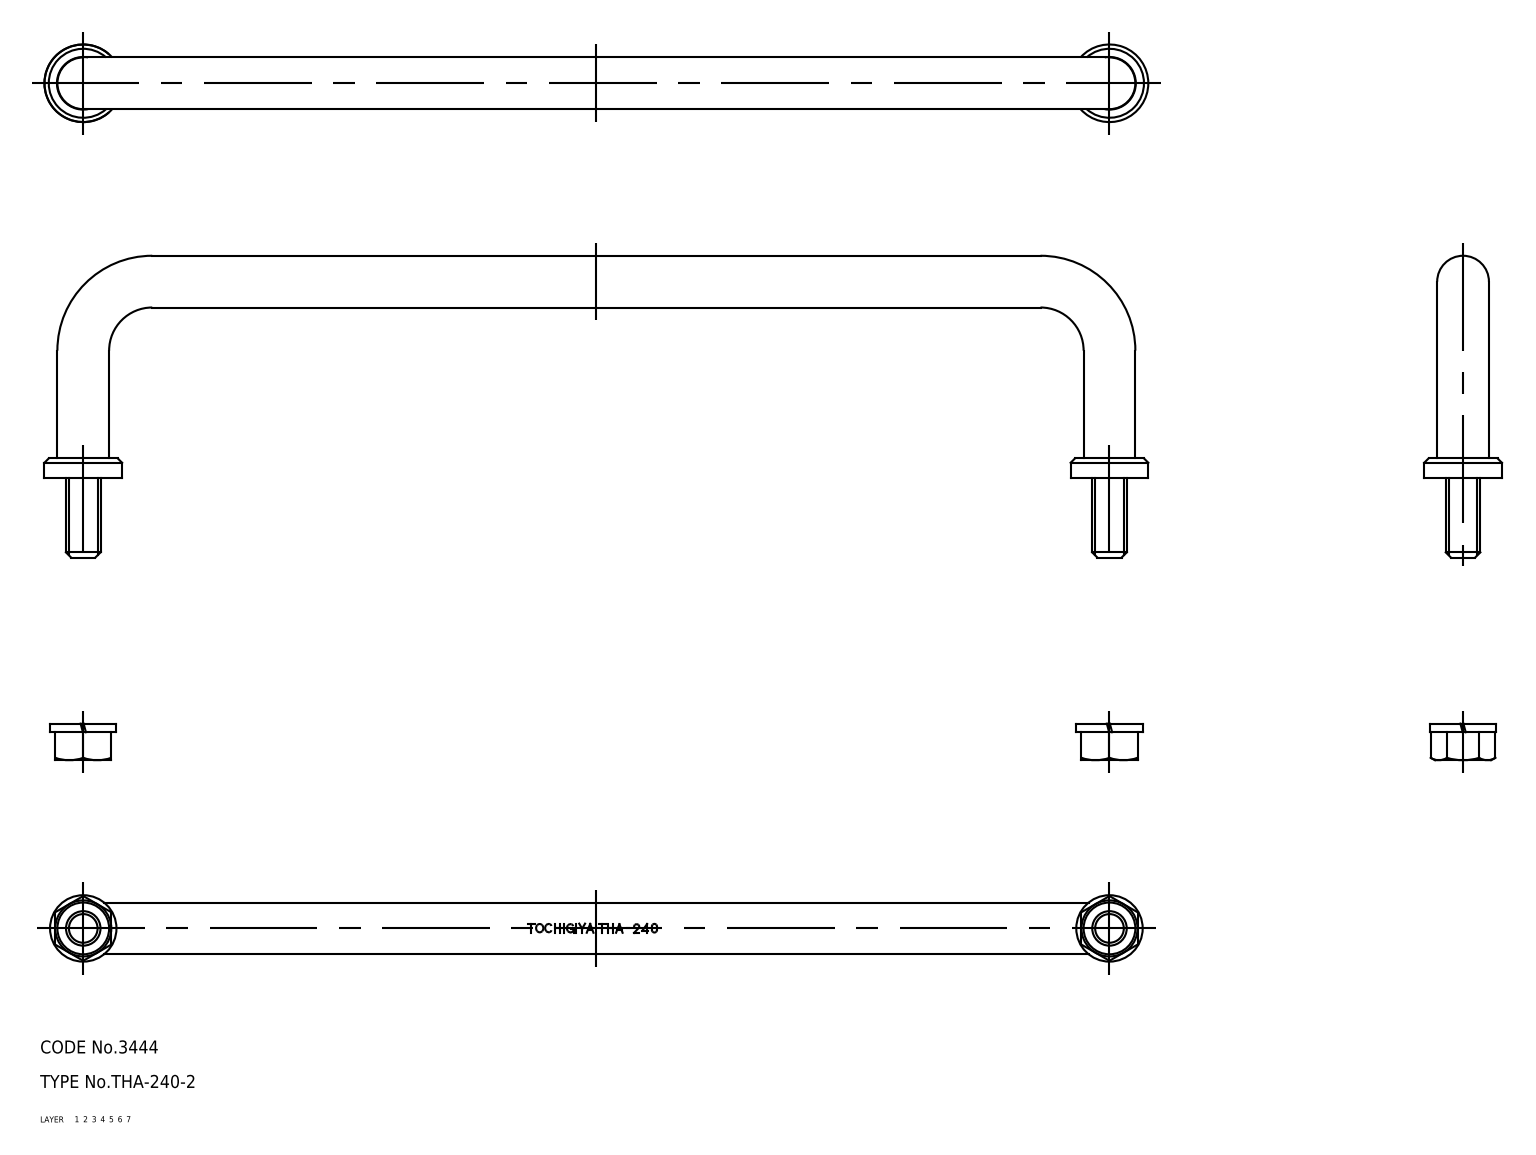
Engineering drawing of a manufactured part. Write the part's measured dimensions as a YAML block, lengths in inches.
part_name: "washer; nut; facing ring; pull (+1 more)"
step_written_by: "CADfix (AUTOMOTIVE_DESIGN)"
units: inches
bodies: {solids: 7, faces: 86, planar: 0, cylindrical: 0, other: 86}
overall_size: [10.079, 2.756, 0.709]
volume: 2.472
surface_area: 25.79
